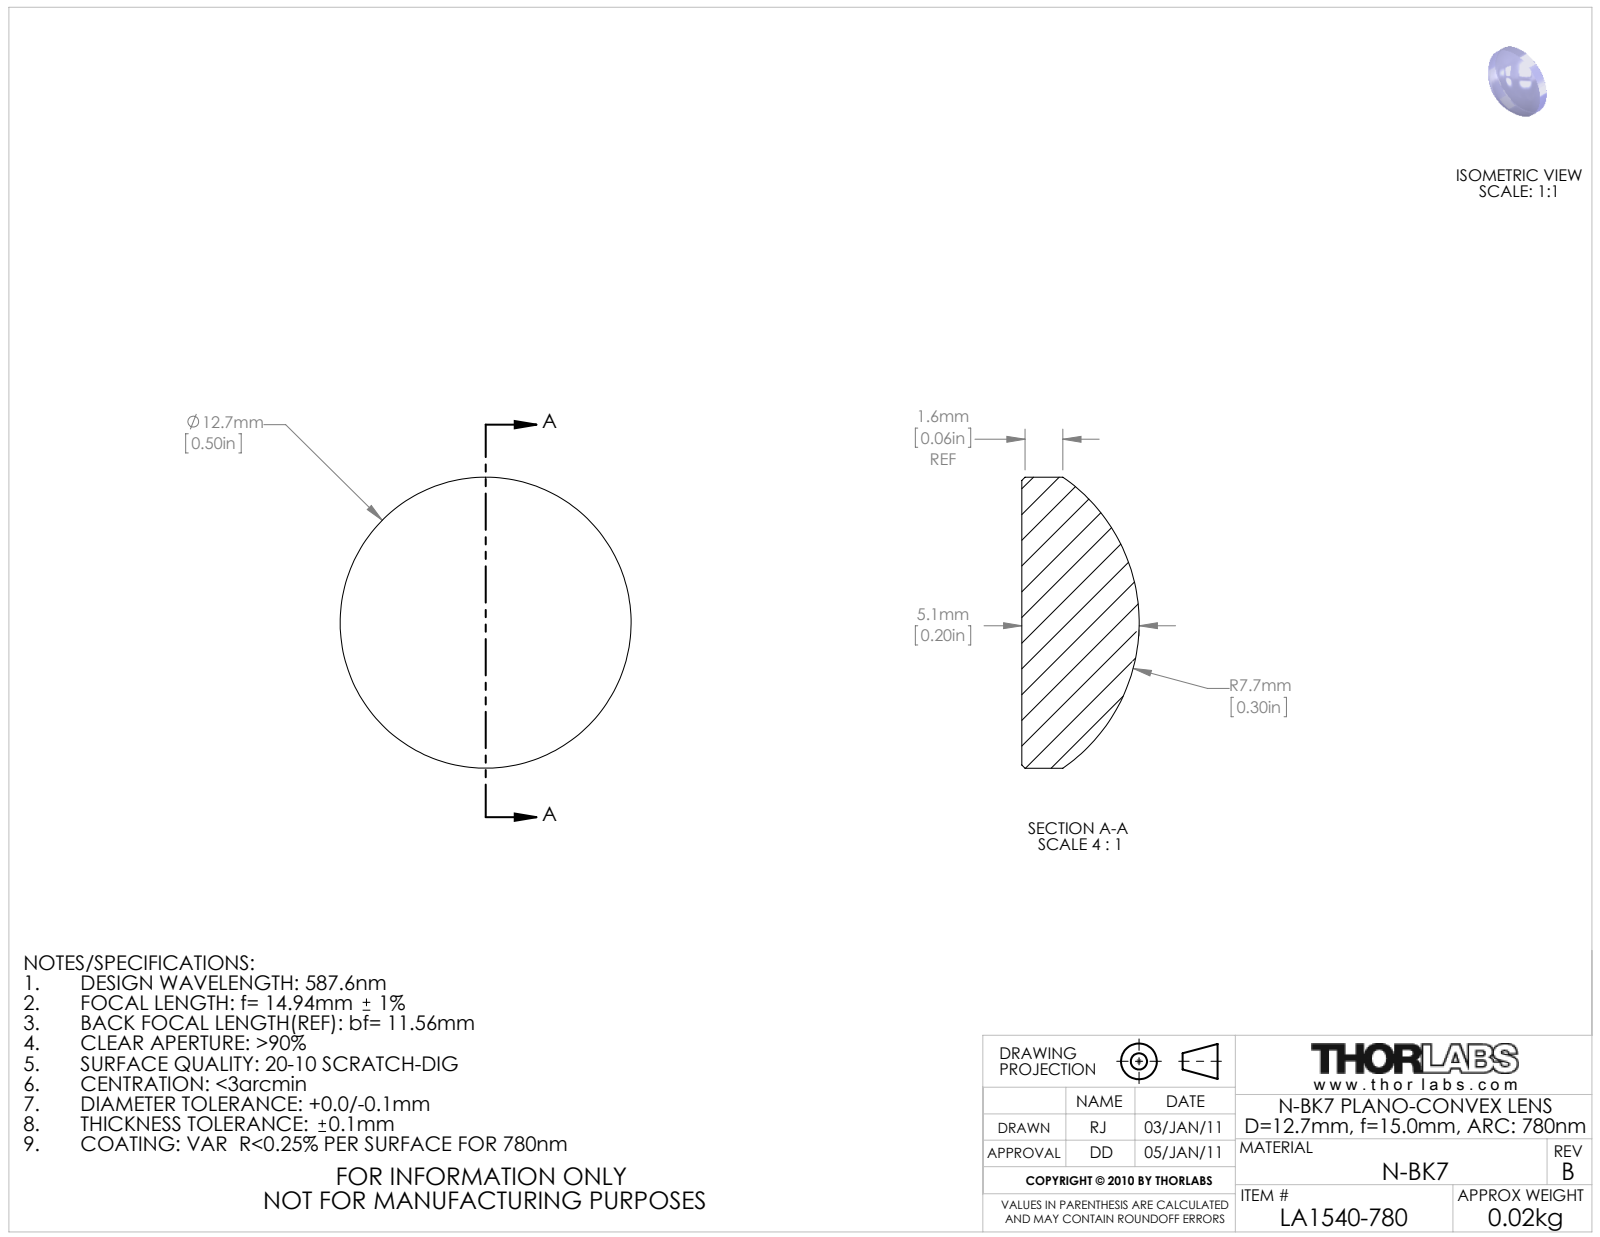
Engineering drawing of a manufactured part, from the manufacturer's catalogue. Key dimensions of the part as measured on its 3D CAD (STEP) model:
Part name (STEP PRODUCT): 21775-E0W
STEP written by: SolidWorks 2011 (AUTOMOTIVE_DESIGN)
Units: millimetres
Bodies: 0 solids, 7 faces (1 planar, 2 cylindrical, 4 other)
Overall size (bounding box): 12.7 × 12.7 × 5.12
Round bosses / shafts (diameter × count): ⌀12.7 ×1
